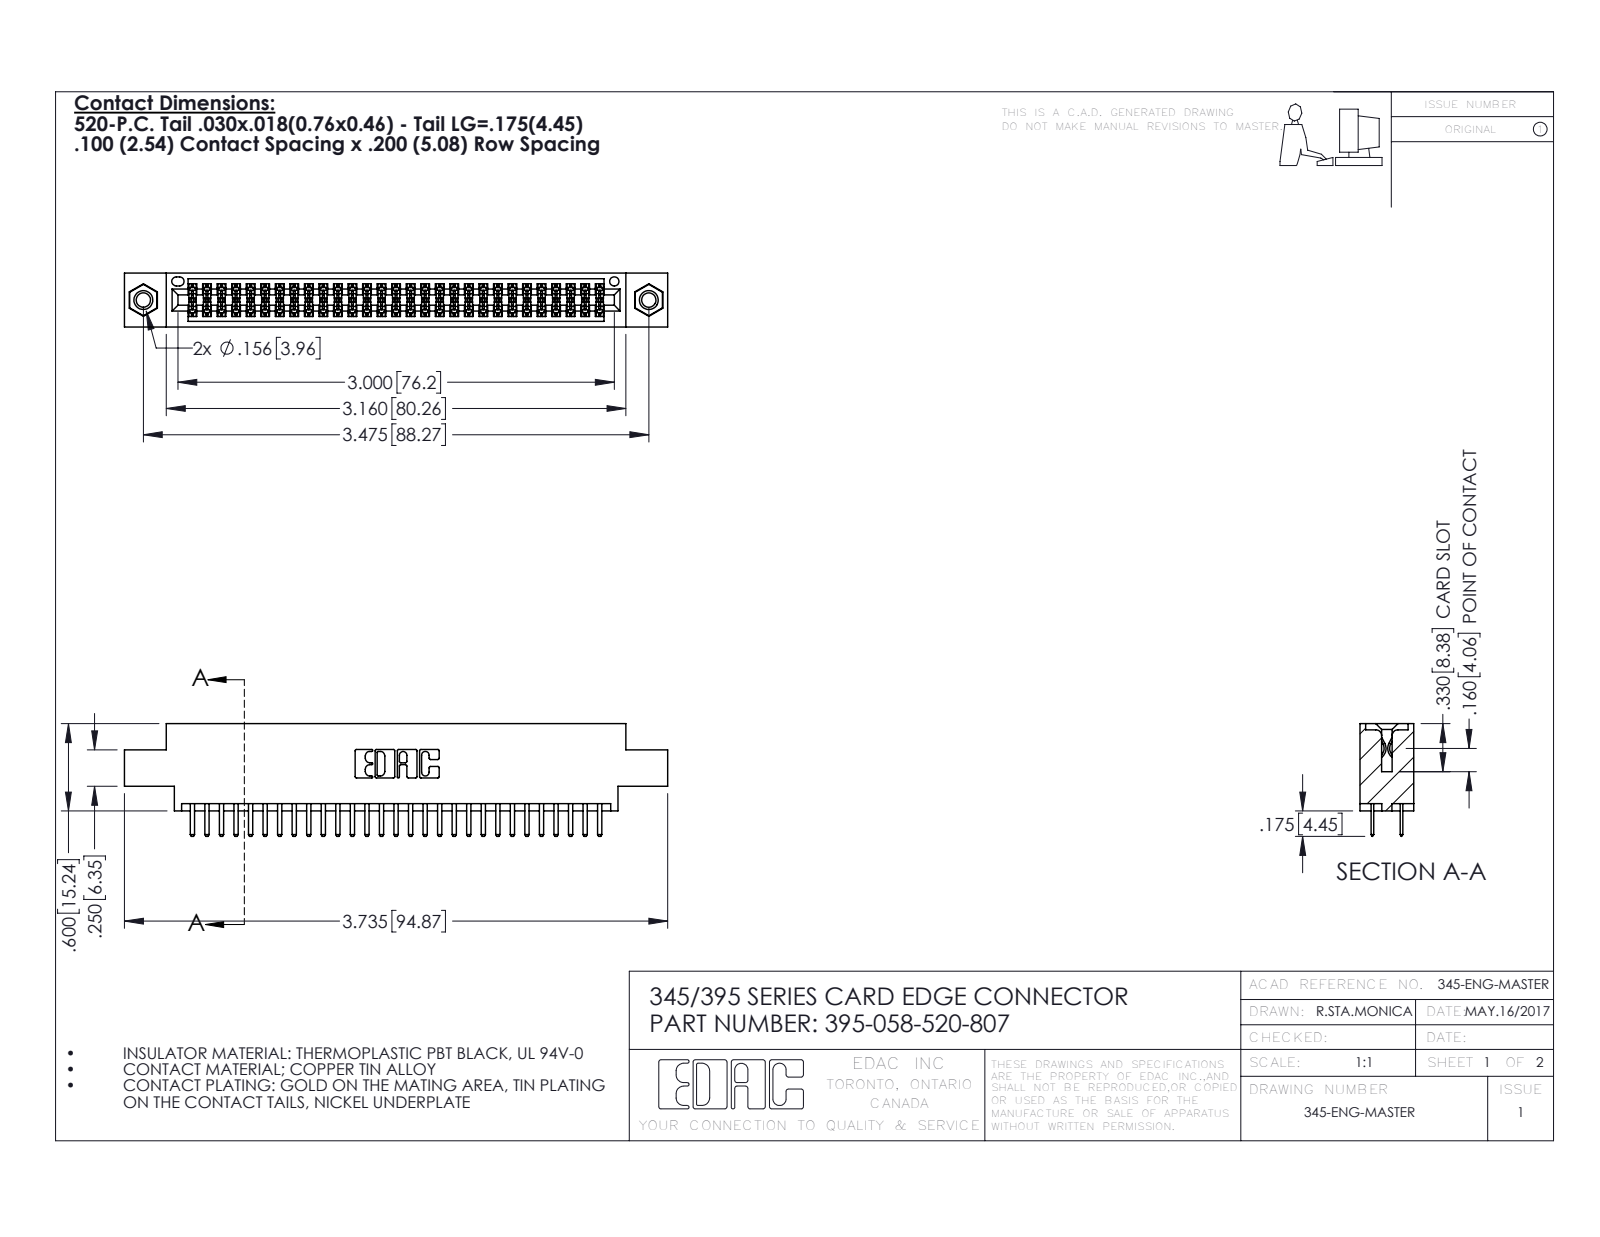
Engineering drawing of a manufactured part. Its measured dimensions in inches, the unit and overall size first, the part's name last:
Units: inches
Overall size (bounding box): 3.735 × 0.775 × 0.37
Round holes (diameter × count): ⌀0.098 ×2, ⌀0.125 ×2, ⌀0.156 ×2, ⌀0.064 ×1
Round bosses / shafts (diameter × count): ⌀0.155 ×2
Partial cylindrical surfaces — rounded edges, fillets, slot ends (radius × count): R0.006 ×87, R0.01 ×62, R0.01 ×22, R0.007 ×6, R0.031 ×6, R0.026 ×3, R0.014 ×2, R0.019 ×2
Main face-to-face distances: 0.072, 0.298, 0.2, 0.37, 0.098, 0.272, 0.025, 0.225, 0.022, 0.175
Hole centre spacings: 0.27, 3.24, 3.475
Volume: 0.546 in³ · Surface area: 20.28 in²
Bodies: 61 solids, 3322 faces (2146 planar, 1160 cylindrical, 16 other)
Part name (STEP PRODUCT): 345 Part_0.170 Offset - 0.156 Dia-TI; 345-292-001_345-293-120; 345-250-001_345-250-005-103; 395-058-520-807
STEP written by: SolidWorks 2016 (CONFIG_CONTROL_DESIGN)
